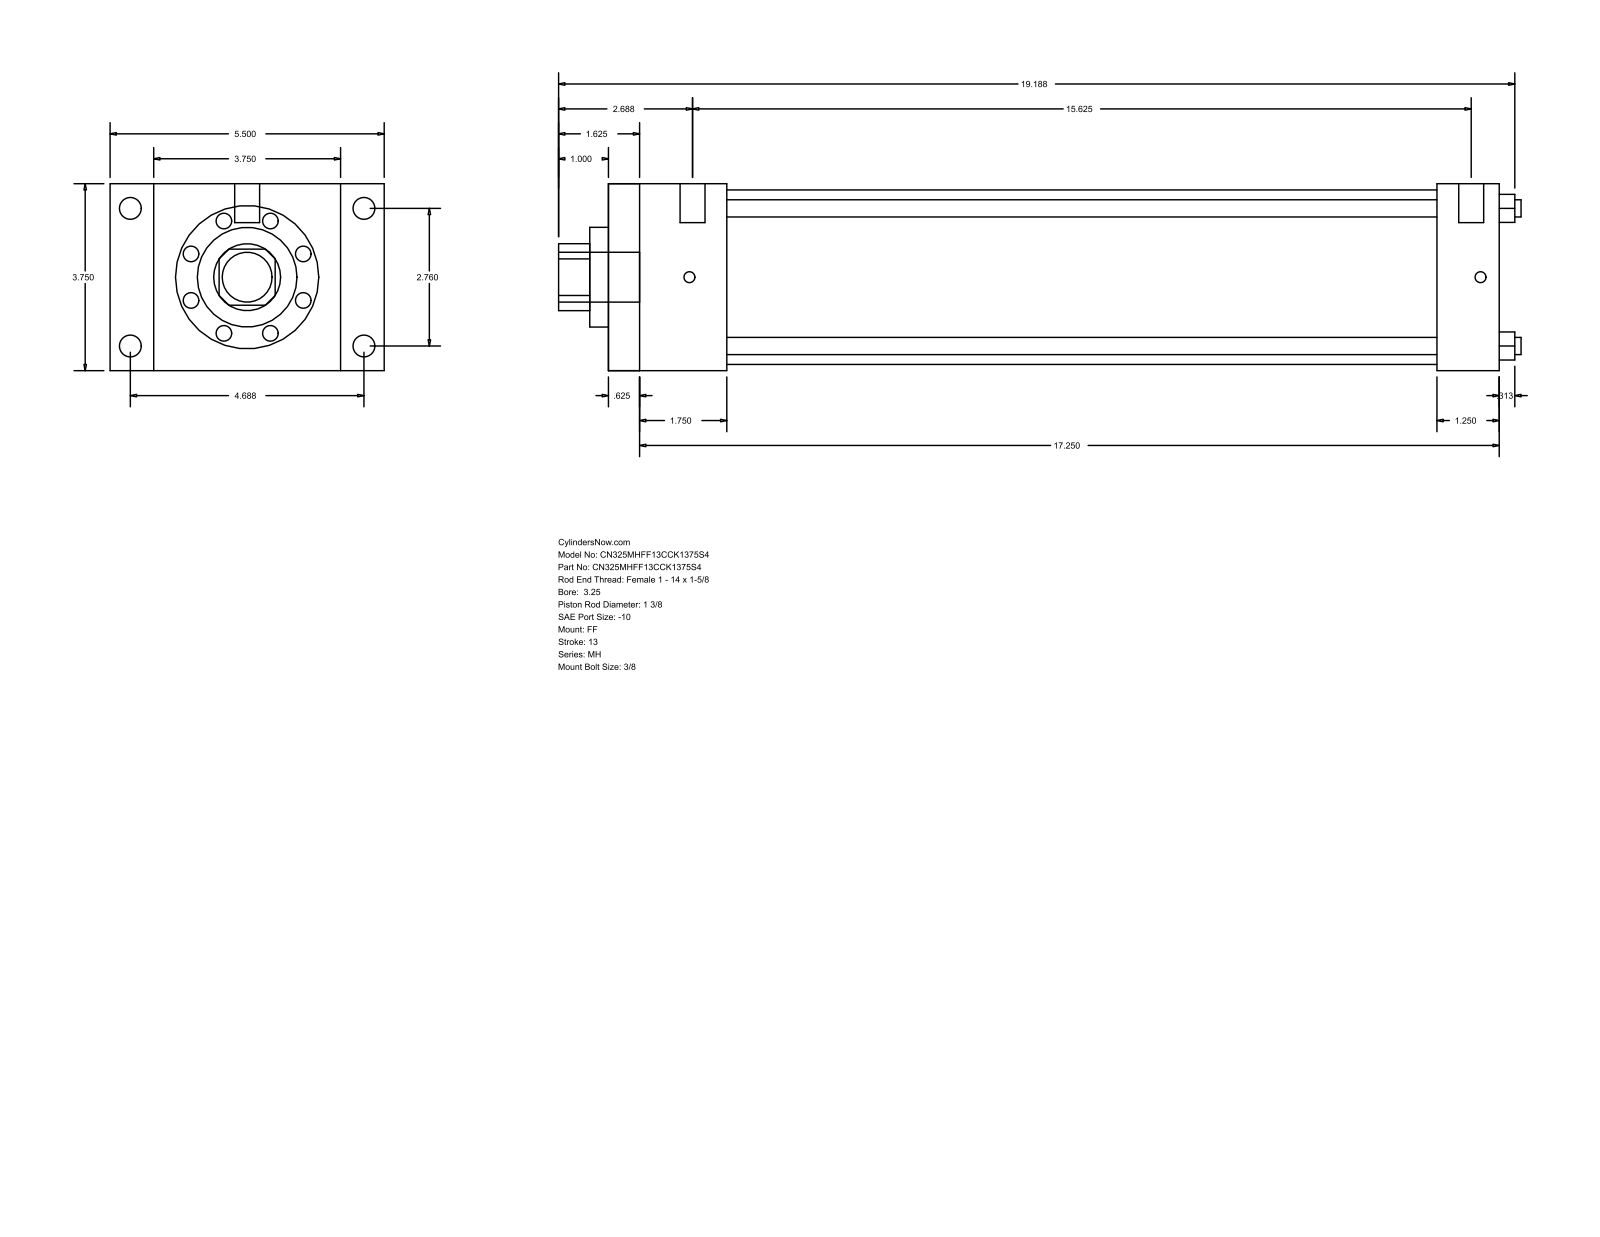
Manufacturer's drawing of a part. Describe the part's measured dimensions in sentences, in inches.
The part is named "MH_FF__0325_1.375". Its 3-D file was written by "GSSL Pune (CONFIG_CONTROL_DESIGN)". It is 0 solids with 92 faces: 64 planar, 28 cylindrical and 0 other. Overall it measures 19.313 by 5.5 by 3.75 inches. Round holes: 4 of diameter 0.345, 1 of diameter 1.375, 1 of diameter 2, 1 of diameter 3.5. Round bosses or shafts: 4 of diameter 0.438, 4 of diameter 0.219, 2 of diameter 0.5, 1 of diameter 1. Partial cylindrical surfaces (rounded edges, fillets, slot ends): 1 of radius 0.672. The main face-to-face distances are 3.75, 17.875, 0.625, 17.25, 0.875, 4.625, 16.625, 16, 1.25, 2.375. The hole center spacings are 1.952, 2.76, 3.903.
